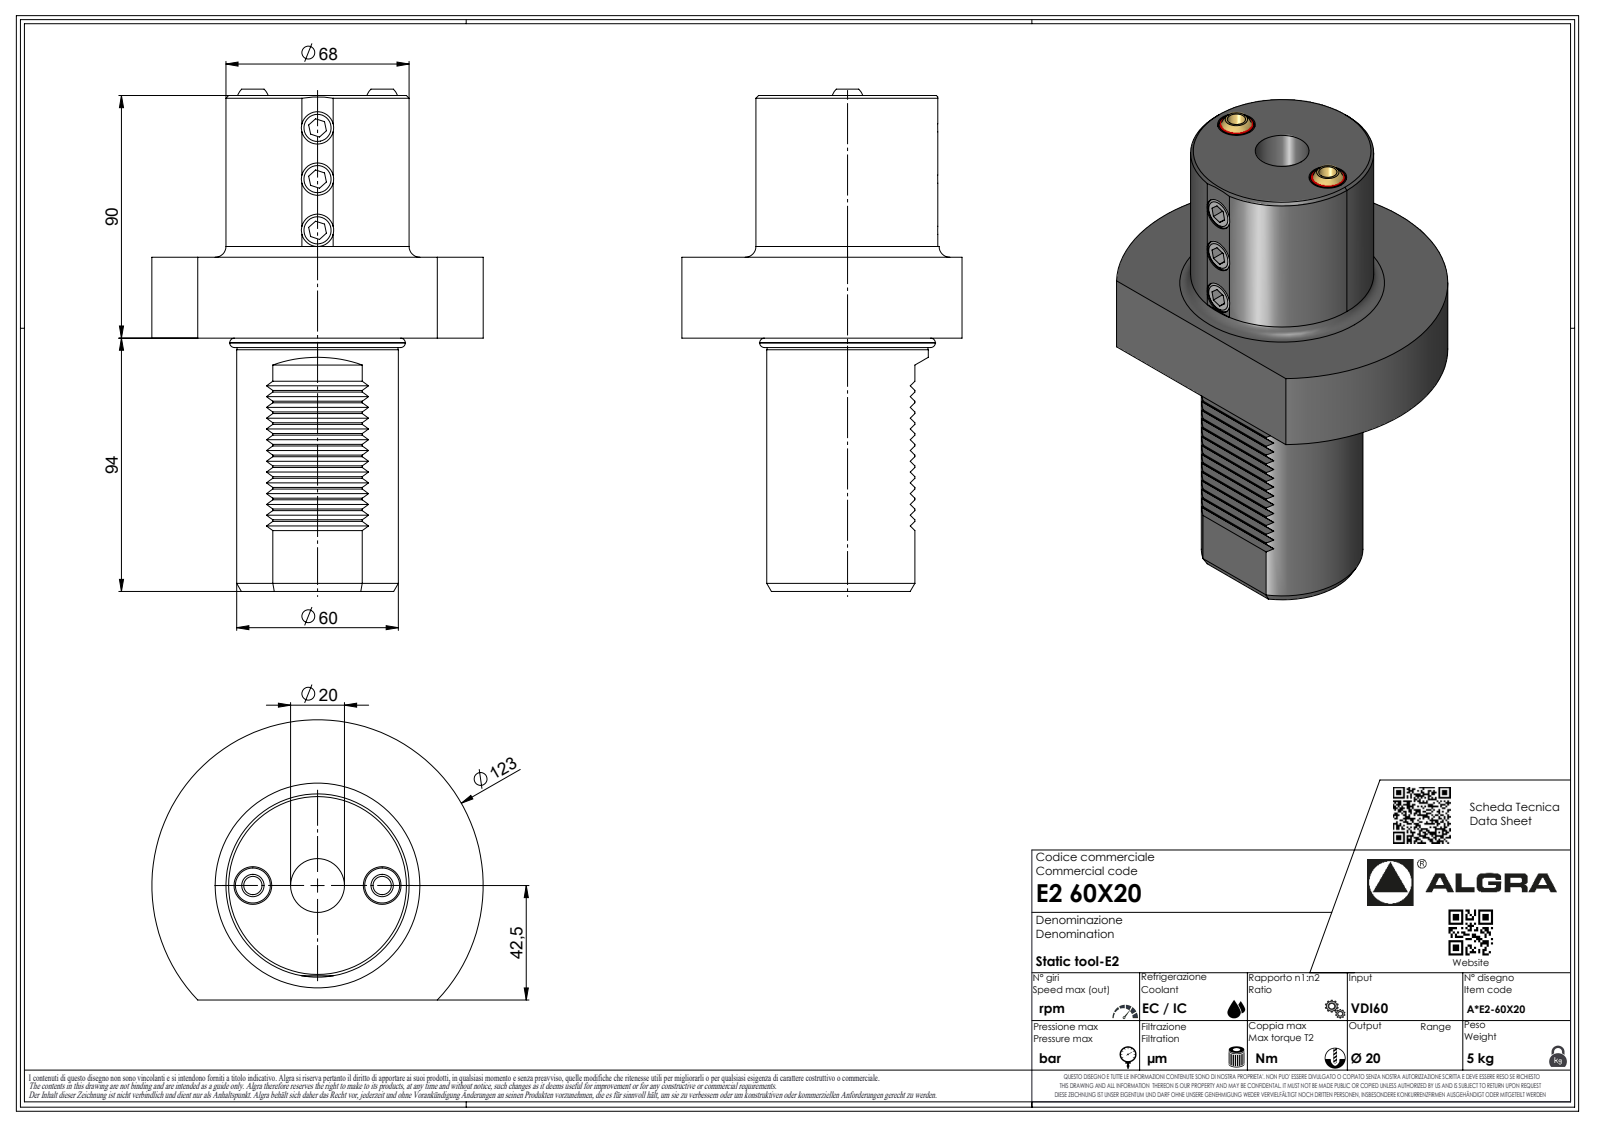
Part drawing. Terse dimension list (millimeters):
name: E260X20
written by: SolidWorks 2023 (AUTOMOTIVE_DESIGN)
unit: mm
bodies: 1 solid, 299 faces (201 planar, 41 cylindrical, 57 other)
size: 186.37 × 123 × 104
volume: 772 340 mm³; area: 69 276 mm²
holes: 3× ⌀12, 1× ⌀2.1, 1× ⌀20
bosses: 1× ⌀68, 1× ⌀65.39, 1× ⌀60, 1× ⌀6.37, 1× ⌀1.7
rounds: 7× R0.33, 7× R0.52, 7× R3.7, 1× R0.21, 1× R33, 1× R61.5
face distances: 30, 60, 90, 184, 124, 94, 2.83, 14.14, 11.31, 5.66
hole spacings: 19, 24.28, 38, 42.2, 60.78
